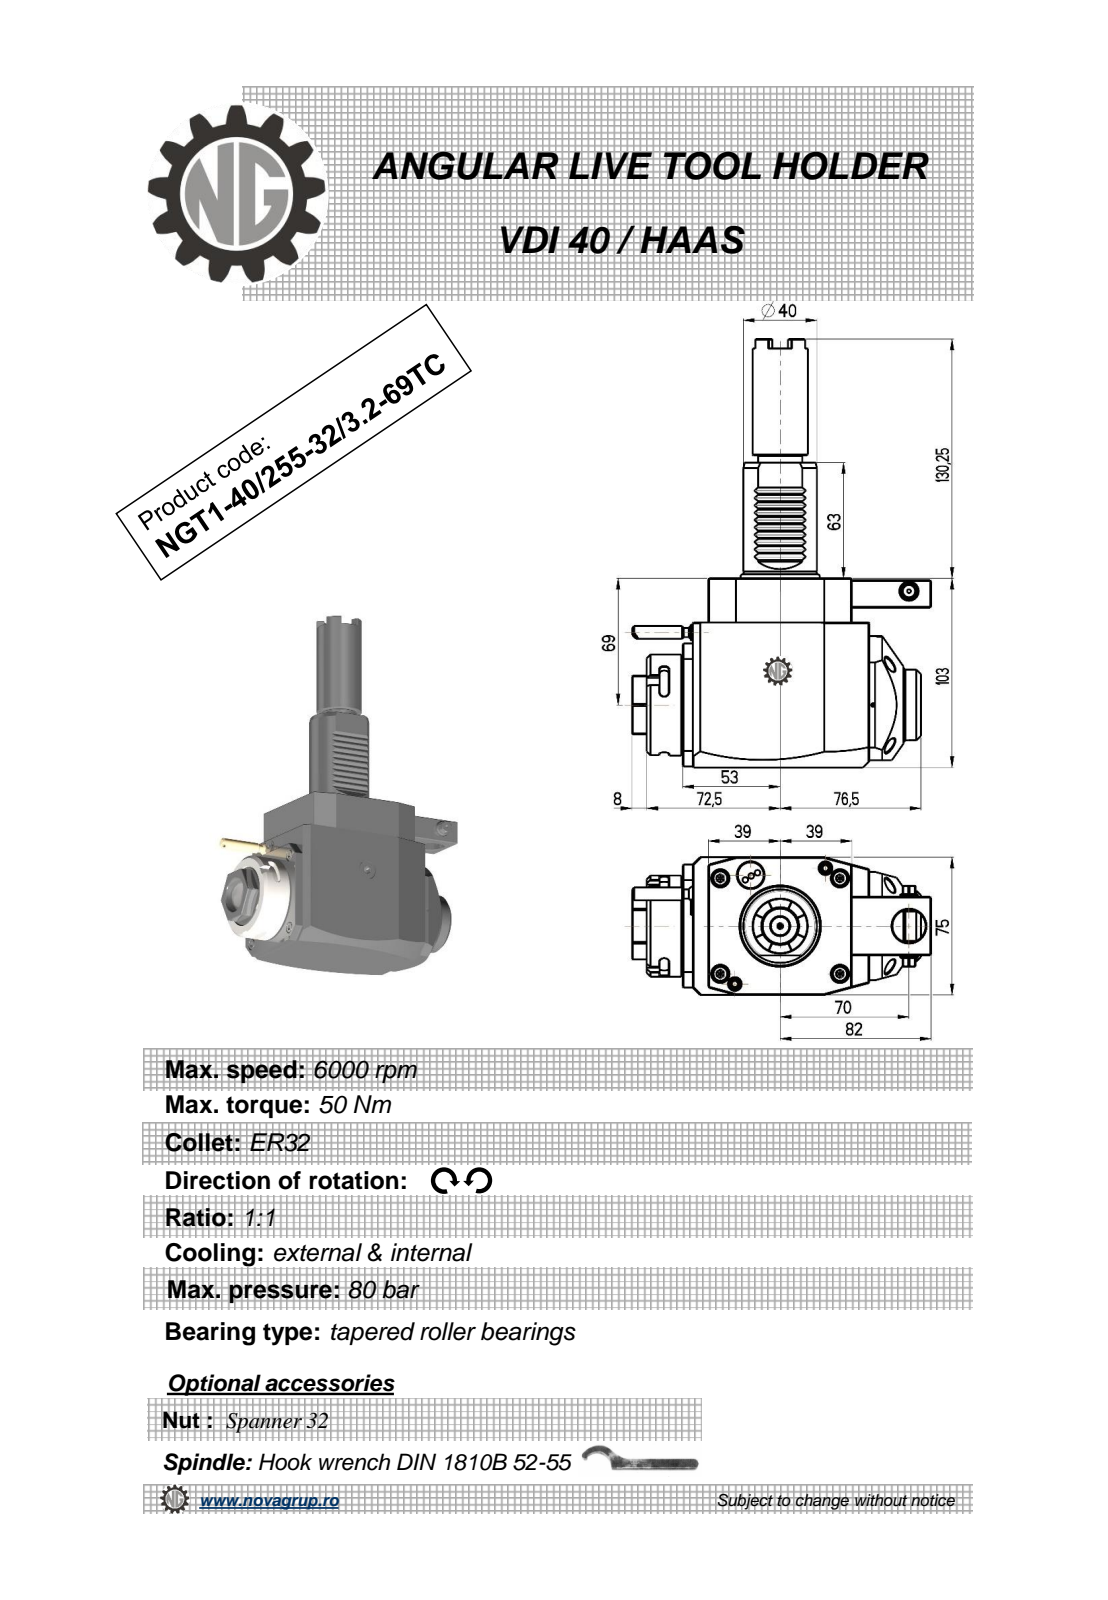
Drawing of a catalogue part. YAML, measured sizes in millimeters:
part_name: "NGT1_40_255_32_3_2_69TC"
step_written_by: "PRO/ENGINEER BY PARAMETRIC TECHNOLOGY CORPORATION, 2010280 (CONFIG_CONTROL_DESIGN)"
units: millimeters
bodies: {solids: 1, faces: 391, planar: 219, cylindrical: 82, other: 90}
overall_size: [233.25, 162.5, 75]
volume: 957182
surface_area: 78396
round_holes:
  - {diameter: 2, count: 1}
  - {diameter: 2.5, count: 1}
  - {diameter: 3, count: 1}
  - {diameter: 9.5, count: 1}
  - {diameter: 18, count: 1}
  - {diameter: 20, count: 1}
  - {diameter: 23, count: 1}
round_bosses_or_shafts:
  - {diameter: 8.96, count: 2}
  - {diameter: 55, count: 1}
  - {diameter: 48, count: 1}
  - {diameter: 40, count: 1}
  - {diameter: 38.5, count: 1}
  - {diameter: 30, count: 1}
  - {diameter: 24, count: 1}
  - {diameter: 10, count: 1}
partial_cylinders:
  - {radius: 0.3, count: 10}
  - {radius: 2.5, count: 6}
  - {radius: 180, count: 2}
  - {radius: 0.5, count: 1}
  - {radius: 3.85, count: 1}
  - {radius: 4.25, count: 1}
  - {radius: 24.5, count: 1}
  - {radius: 37.5, count: 1}
face_to_face_distances: [75, 103, 33.5, 19.5, 79, 8, 14, 102, 21.5, 87]
hole_center_spacings: [28.11, 43.2, 61.5, 70]
